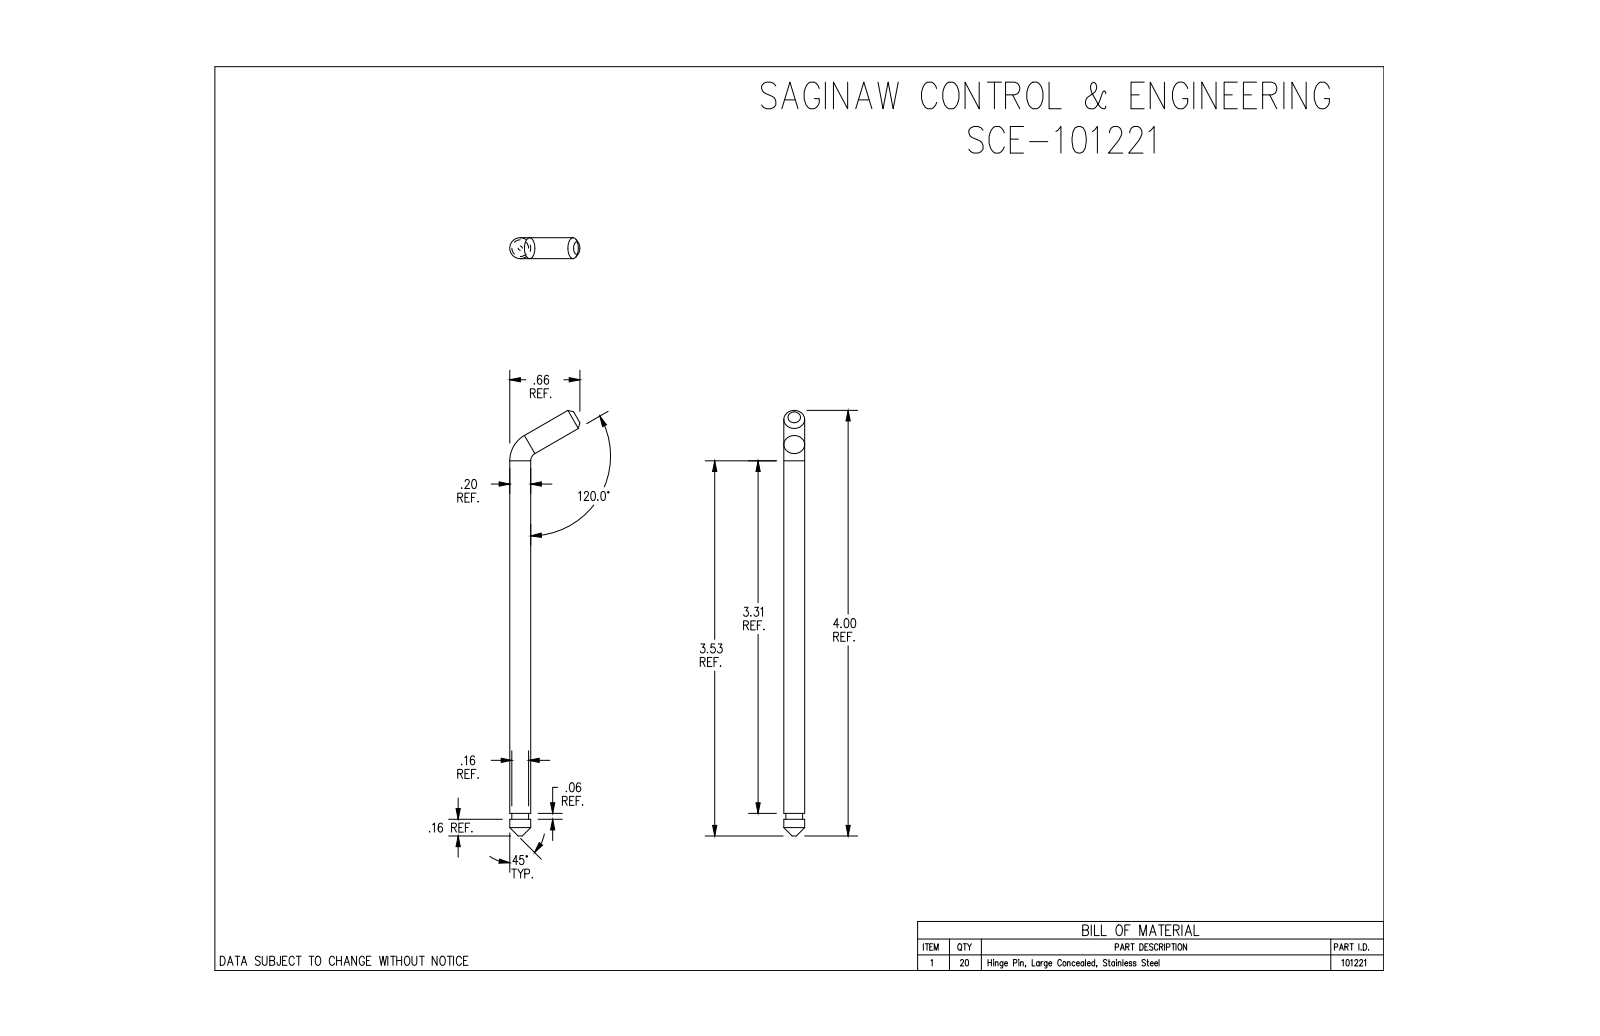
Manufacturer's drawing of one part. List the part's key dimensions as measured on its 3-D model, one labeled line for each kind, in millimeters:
Part name (STEP PRODUCT): SCE-101221
STEP written by: SolidWorks 2019 (AUTOMOTIVE_DESIGN)
Units: millimetres
Bodies: 1 solid, 11 faces (4 planar, 4 cylindrical, 3 other)
Overall size (bounding box): 101.7 × 16.8 × 5
Volume: 2 060 mm³ · Surface area: 1 701 mm²
Round bosses / shafts (diameter × count): ⌀5 ×2, ⌀4 ×1
Main face-to-face distances: 1.4, 5.4, 4
